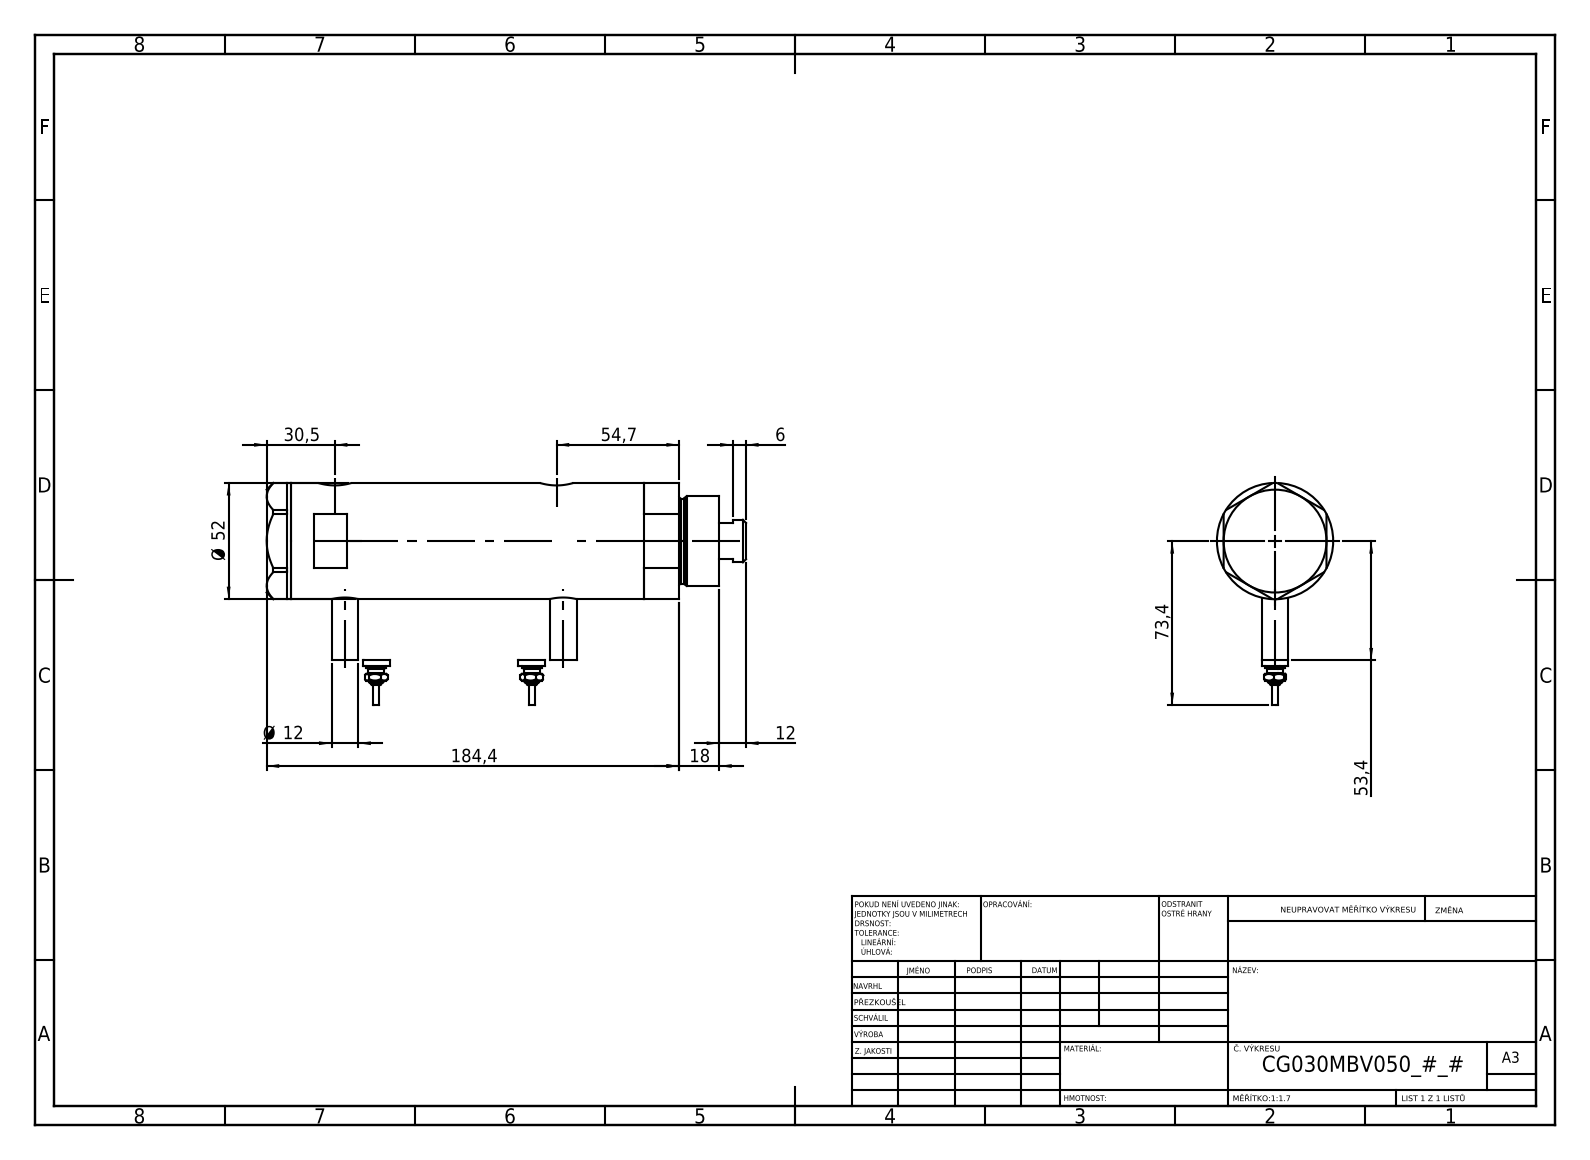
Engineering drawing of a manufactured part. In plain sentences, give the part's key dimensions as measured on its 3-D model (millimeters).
The part is named "Switch; V270CG_MIDDLE; V270CG_BACK; V270CG_VC (+1 more)". Its 3-D file was written by "SolidWorks 2019 (CONFIG_CONTROL_DESIGN)". It is 6 solids with 226 faces: 93 planar, 69 cylindrical and 64 other. Overall it measures 214.4 by 99.4 by 52 millimeters. Its volume is 396 792 cubic millimeters and its surface area 89 841 square millimeters. Round holes: 2 of diameter 9.73, 2 of diameter 12.5, 2 of diameter 15, 1 of diameter 6.5, 1 of diameter 20, 1 of diameter 21.5, 1 of diameter 30, 1 of diameter 33, 1 of diameter 44. Round bosses or shafts: 4 of diameter 12, 2 of diameter 9, 2 of diameter 7, 2 of diameter 4.5, 2 of diameter 2.5, 1 of diameter 52, 1 of diameter 40, 1 of diameter 38. The main face-to-face distances are 121.5, 23.8, 97.7, 11, 34.8, 132.5, 46, 36.4, 168.9, 157.9. The hole center spacings are 2.9, 4.5, 94.7, 97.6, 99.2, 102.1.
